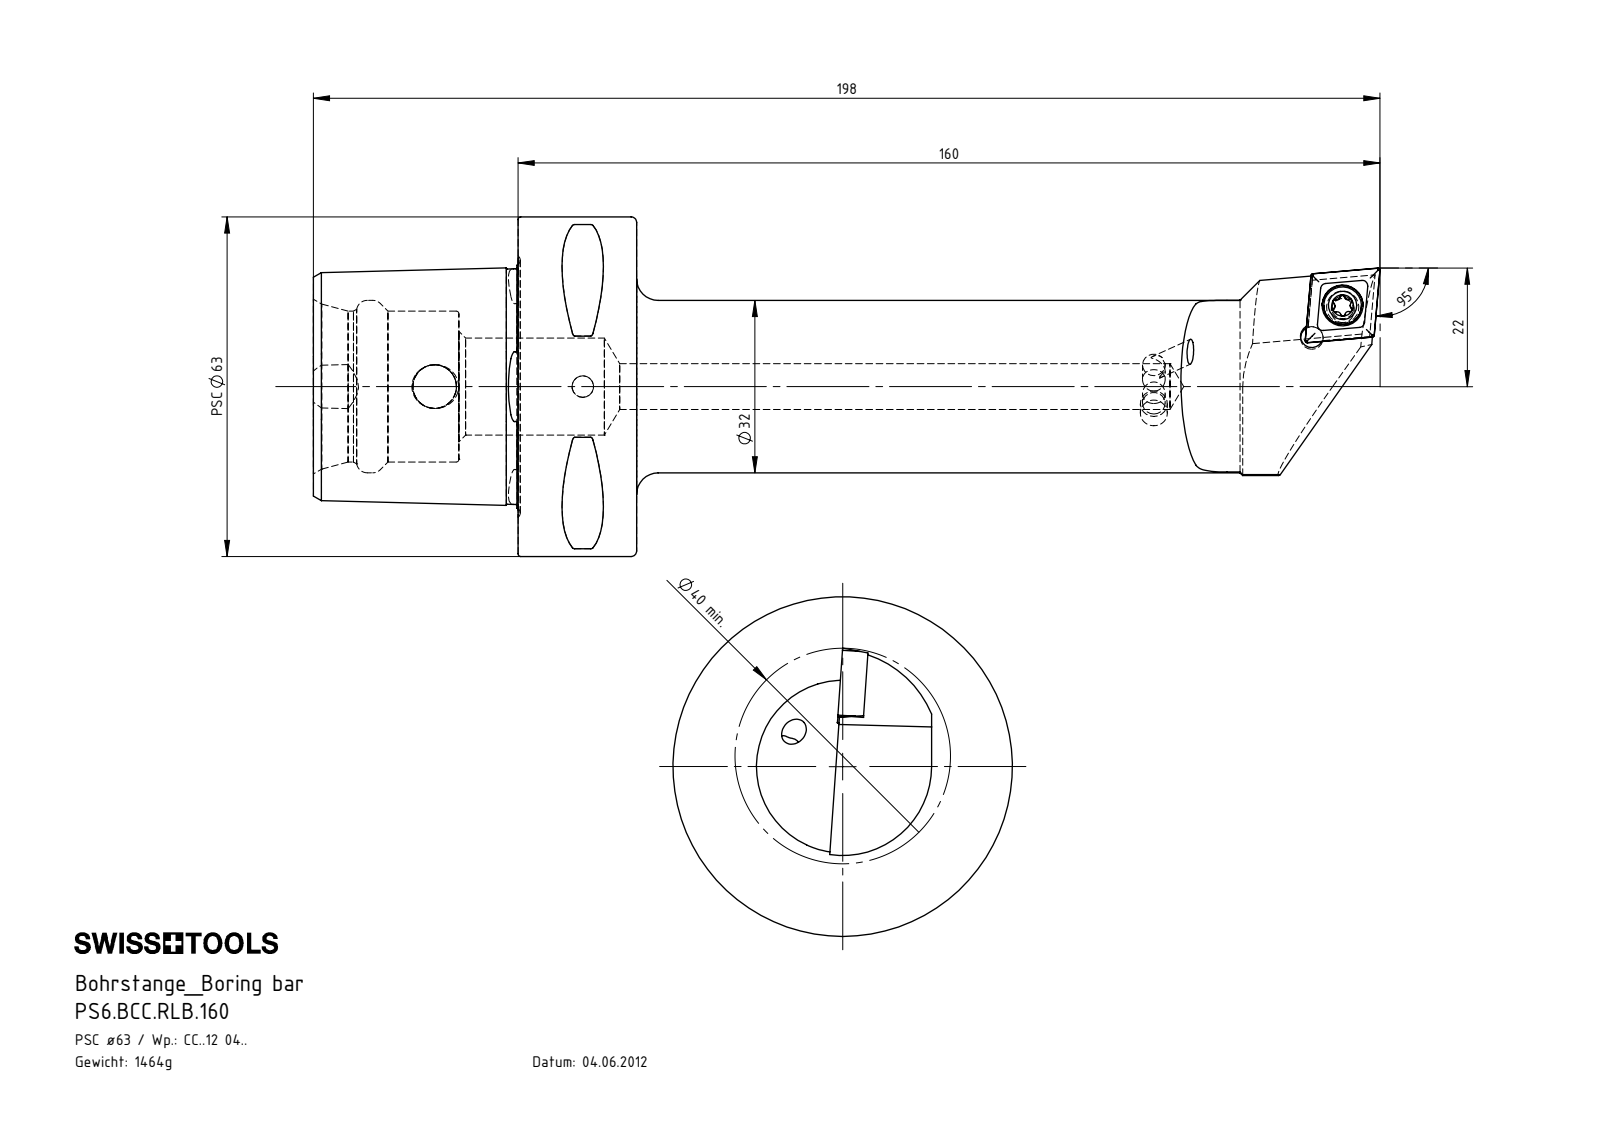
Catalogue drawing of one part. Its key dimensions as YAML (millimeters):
part_name: "PS6.BCC.RLB.160; KVT_MB_600_050; CCMT120404; PS6-BCC.RLB.160_A (+1 more)"
step_written_by: "SolidWorks 2017 (AUTOMOTIVE_DESIGN)"
units: millimeters
bodies: {solids: 5, faces: 276, planar: 49, cylindrical: 74, other: 153}
overall_size: [198, 63, 63]
volume: 187743
surface_area: 36967
round_holes:
  - {diameter: 4.2, count: 4}
  - {diameter: 4, count: 2}
  - {diameter: 5.5, count: 1}
  - {diameter: 7.6, count: 1}
  - {diameter: 8.1, count: 1}
  - {diameter: 8.5, count: 1}
  - {diameter: 18, count: 1}
  - {diameter: 28, count: 1}
  - {diameter: 32, count: 1}
round_bosses_or_shafts:
  - {diameter: 5, count: 2}
  - {diameter: 63, count: 1}
  - {diameter: 7, count: 1}
partial_cylinders:
  - {radius: 0.5, count: 8}
  - {radius: 0.39, count: 6}
  - {radius: 0.69, count: 3}
  - {radius: 0.69, count: 3}
  - {radius: 3, count: 1}
  - {radius: 6, count: 1}
  - {radius: 16.5, count: 1}
  - {radius: 19, count: 1}
face_to_face_distances: [22, 38, 60, 24.88, 27, 11, 33, 4.45, 55.8, 37.8]
hole_center_spacings: [8.09, 27.5]
